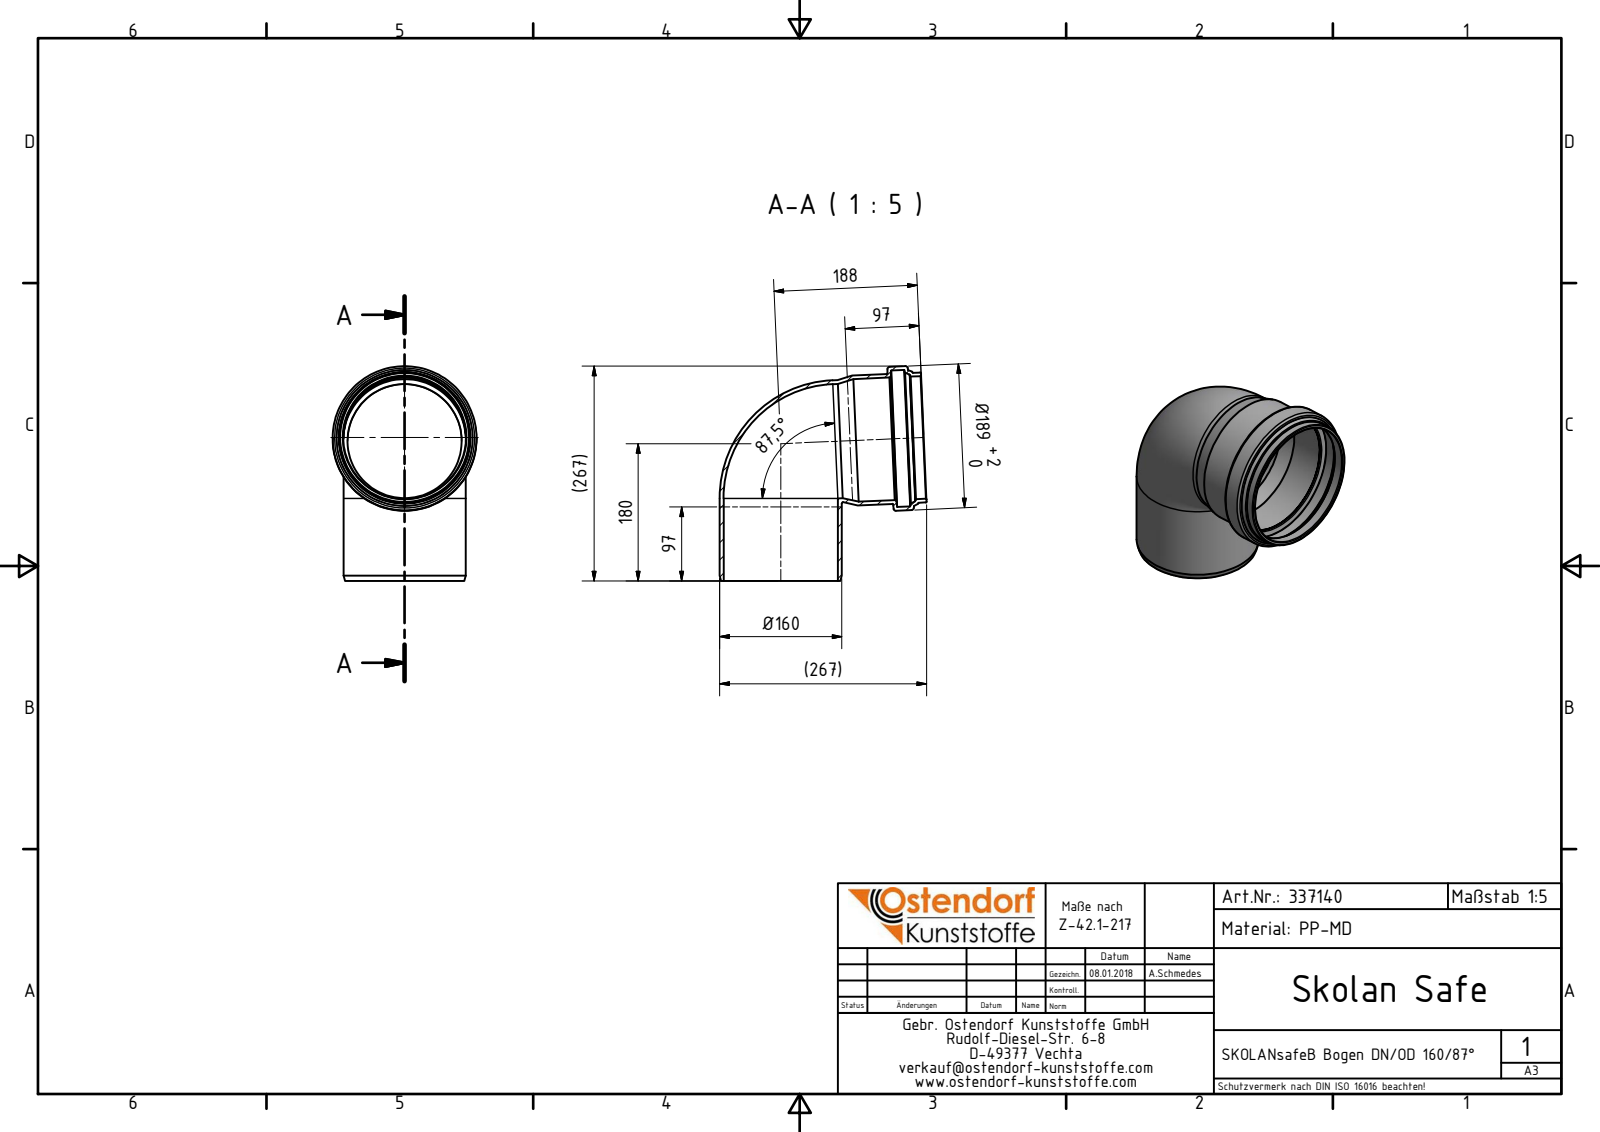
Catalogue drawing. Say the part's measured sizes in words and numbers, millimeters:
The part is named "337140 SKOLANsafeB Bogen DN_OD 160_87°". Its 3-D file was written by "Autodesk Inventor 2016 (AUTOMOTIVE_DESIGN)". It is 1 solid with 41 faces: 3 planar, 11 cylindrical and 27 other. Overall it measures 281.74 by 271.65 by 189 millimeters. Its volume is 808 904 cubic millimeters and its surface area 358 300 square millimeters. Round holes: 2 of diameter 149.9, 2 of diameter 161, 1 of diameter 161.2, 1 of diameter 179.4. Round bosses or shafts: 2 of diameter 170.6, 2 of diameter 160.3, 1 of diameter 189. The main face-to-face distances are 41.79.
